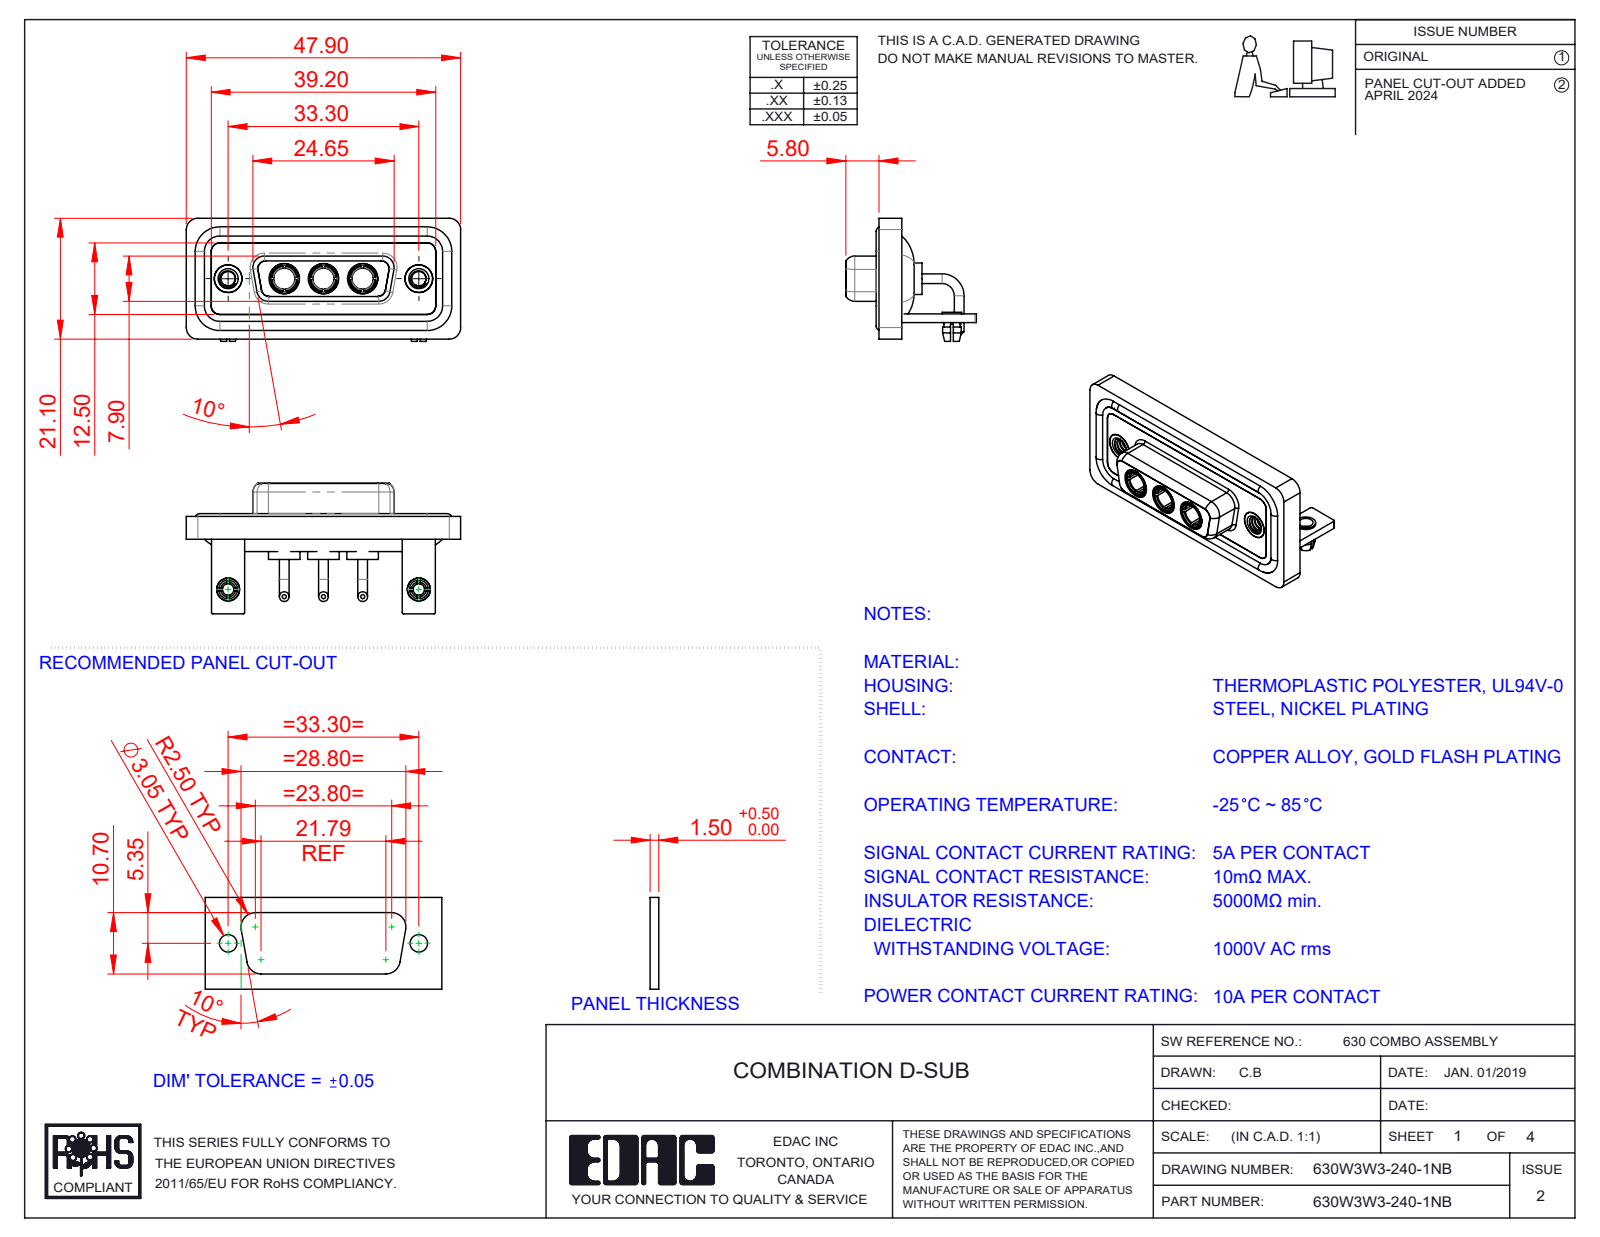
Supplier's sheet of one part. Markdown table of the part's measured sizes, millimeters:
| quantity | value |
| --- | --- |
| part name | 630Combo Board Lock_50 Contacts; 630Combo Shell Front_15 Contacts; Power Socket_10A RA; 630Combo Housing_3W3 (+5 more) |
| STEP written by | SolidWorks 2023 (CONFIG_CONTROL_DESIGN) |
| units | millimeters |
| bodies | 17 solids, 754 faces (260 planar, 317 cylindrical, 177 other) |
| overall size | 47.9 × 22.8 × 21.5 |
| volume | 6 402 mm³ |
| surface area | 10 769 mm² |
| round holes (diameter × count) | 4.85 × 5, 2.5 × 4, 3.7 × 3, 5.3 × 3, 2 × 2, 3.2 × 2, 4 × 2, 4.05 × 2, 5 × 2 |
| round bosses / shafts (diameter × count) | 1.7 × 6, 1.6 × 4, 5.5 × 3, 5.2 × 3, 4.96 × 3, 4.75 × 3, 3.75 × 3, 4.95 × 2 |
| partial cylindrical surfaces (radius × count) | 2 × 21, 1.5 × 18, 0.25 × 16, 1.35 × 12, 1.6 × 8, 0.5 × 5, 0.6 × 4, 0.65 × 4 |
| main face-to-face distances | 0.4, 2.9, 1.5, 1.8, 3.7, 1.1, 4.1, 1.6, 2.5, 1.4 |
| hole center spacings | 6.85, 9.8, 16.65, 23.5, 33.3, 13.7 |
